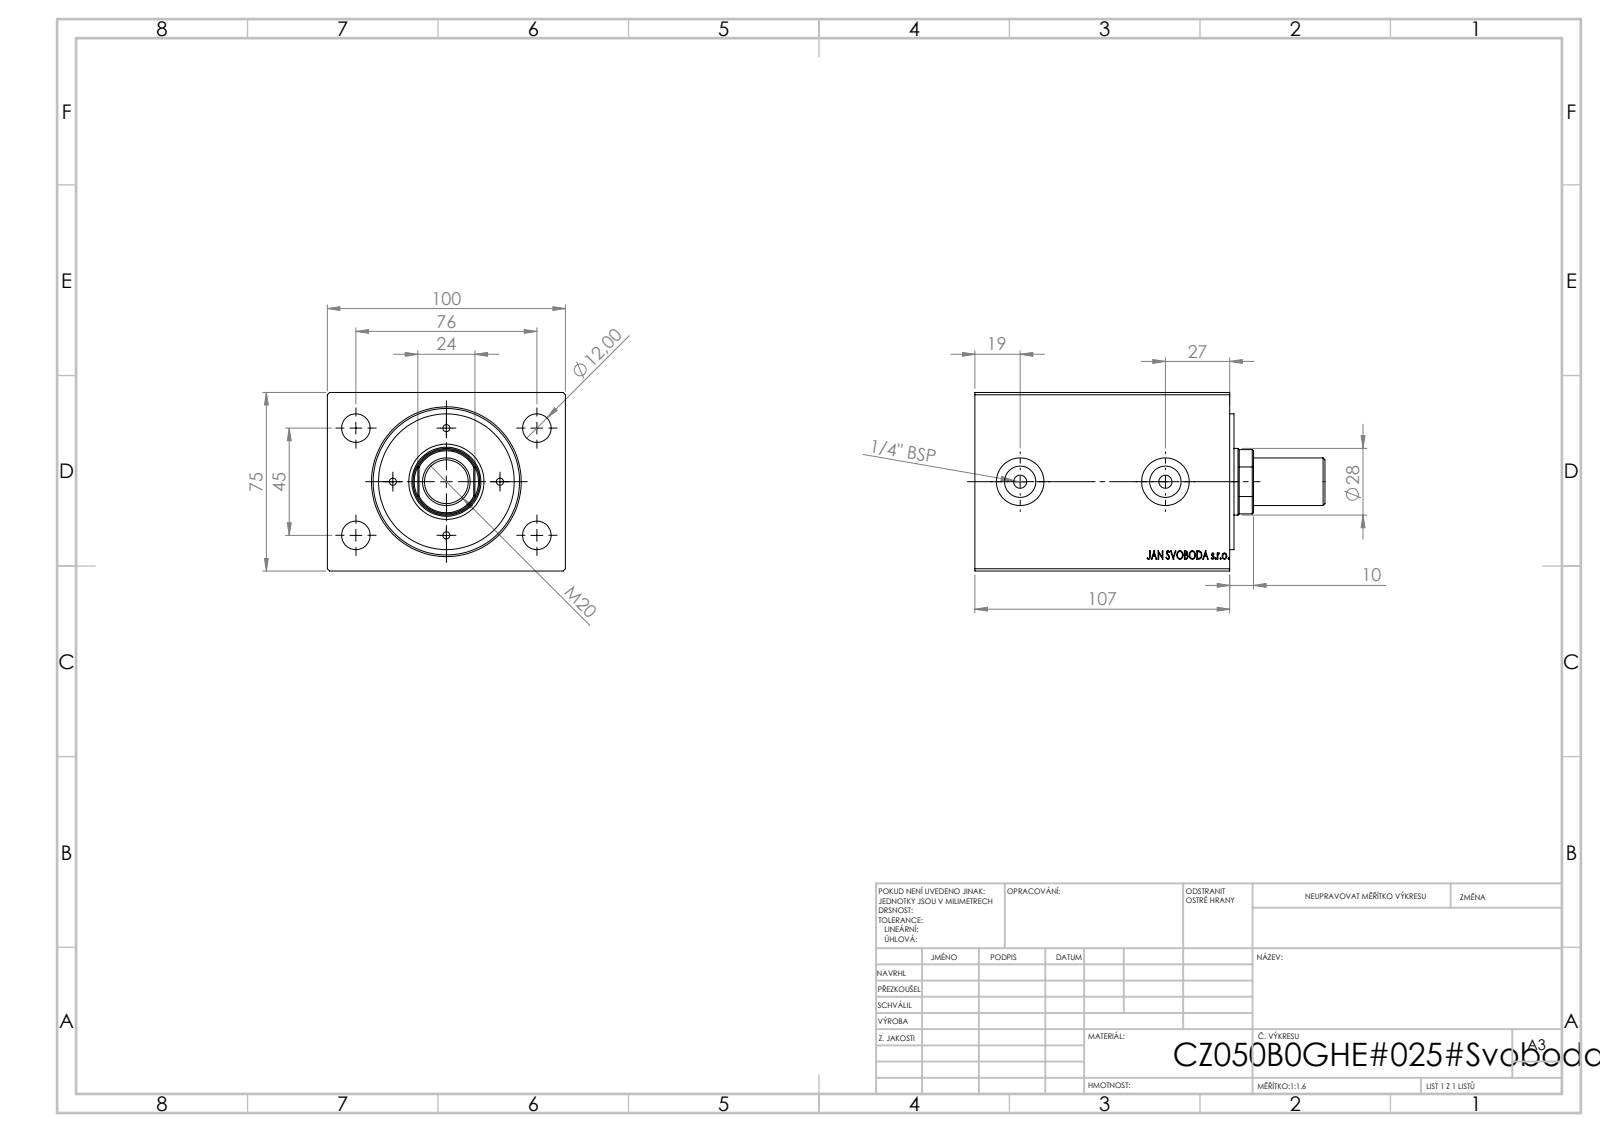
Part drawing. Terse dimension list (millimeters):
name: V500CZ_SMALL_MALE_METRIC; V500CZ_B_VC; V500CZ
written by: SolidWorks 2019 (CONFIG_CONTROL_DESIGN)
unit: mm
bodies: 4 solids, 880 faces (402 planar, 60 cylindrical, 418 other)
size: 147 × 100 × 75
volume: 746 727 mm³; area: 103 500 mm²
holes: 4× ⌀3, 4× ⌀12, 2× ⌀5.5, 2× ⌀13.16, 2× ⌀20, 1× ⌀18.5, 1× ⌀28, 1× ⌀29, 1× ⌀36, 1× ⌀50, 1× ⌀61.5
bosses: 1× ⌀57, 1× ⌀20
rounds: 1× R13.5
face distances: 75, 100, 107, 89.2, 17.8, 10, 8.2, 1.8, 81, 98.8
hole spacings: 22.5, 27.32, 31.82, 38, 44.16, 45, 58.9, 64.55
